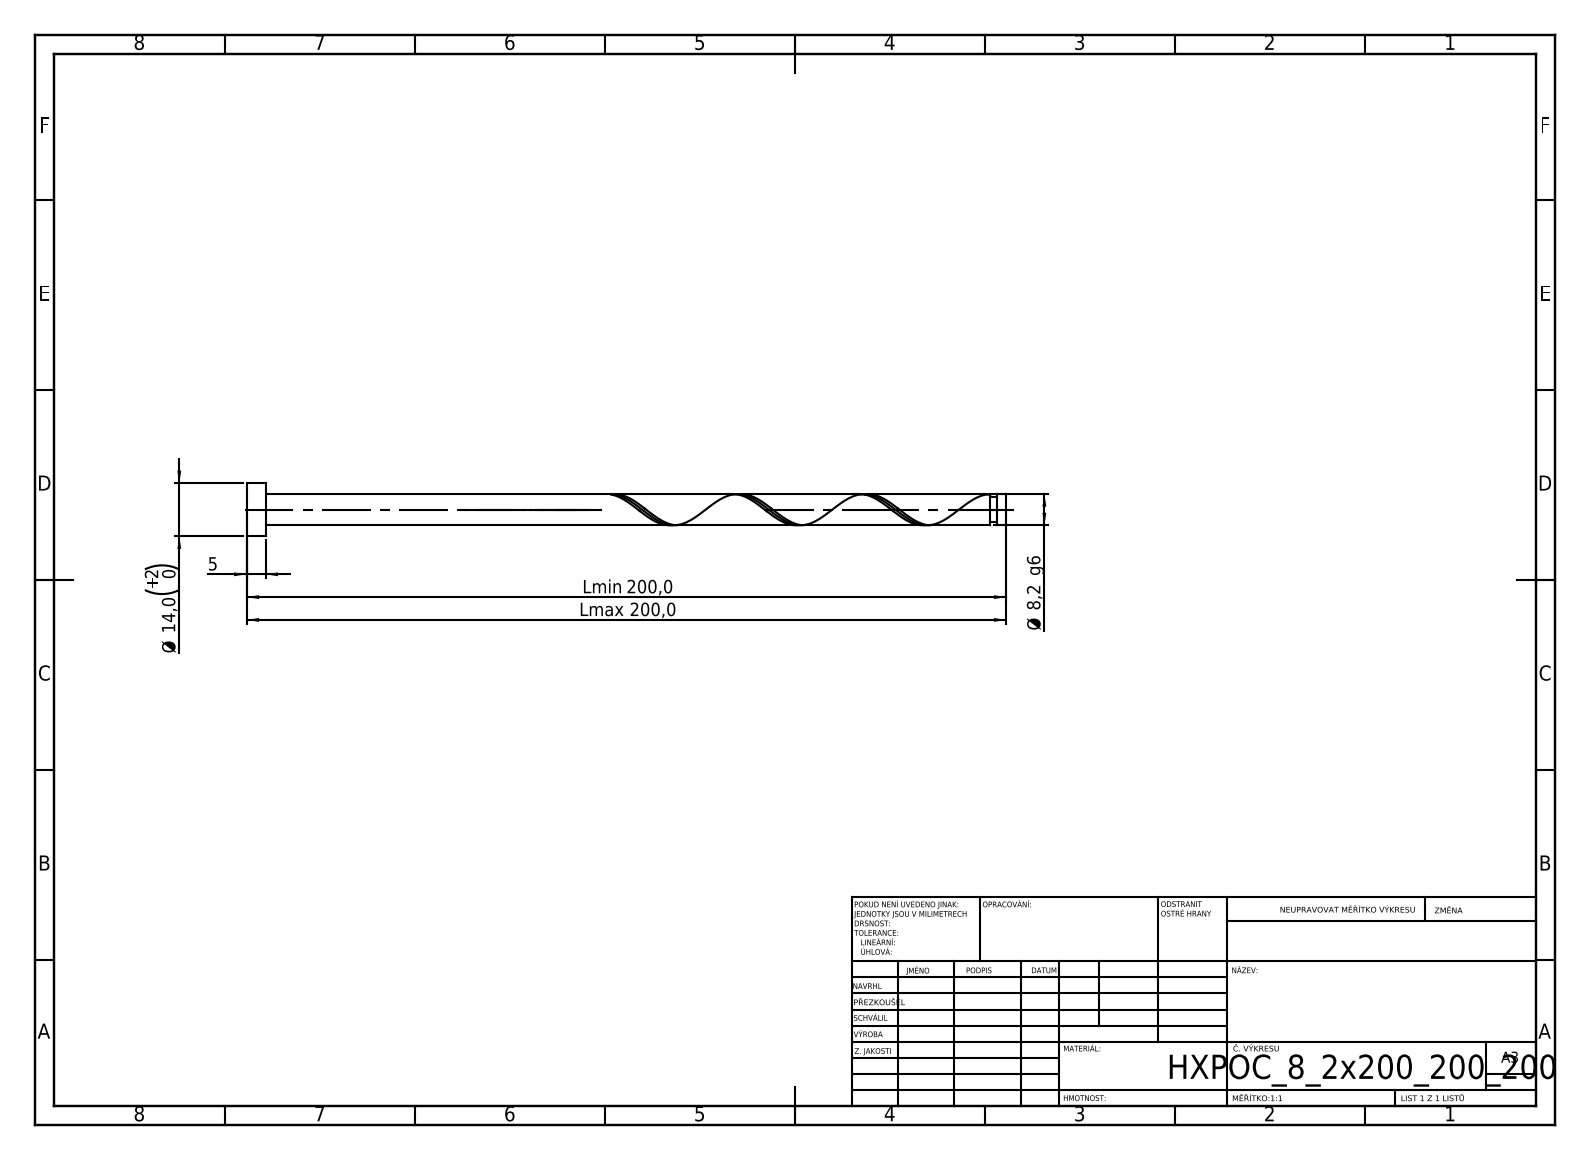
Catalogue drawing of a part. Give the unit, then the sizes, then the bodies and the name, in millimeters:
Units: millimetres
Overall size (bounding box): 200 × 14 × 14
Round bosses / shafts (diameter × count): ⌀14 ×1, ⌀8.2 ×1, ⌀6.56 ×1
Main face-to-face distances: 5, 200, 195, 197.45, 192.45, 2.55, 195.81, 190.81, 1.64, 4.19
Volume: 10 935 mm³ · Surface area: 5 688 mm²
Bodies: 1 solid, 21 faces (6 planar, 14 cylindrical, 1 other)
STEP written by: SolidWorks 2019 (CONFIG_CONTROL_DESIGN)
